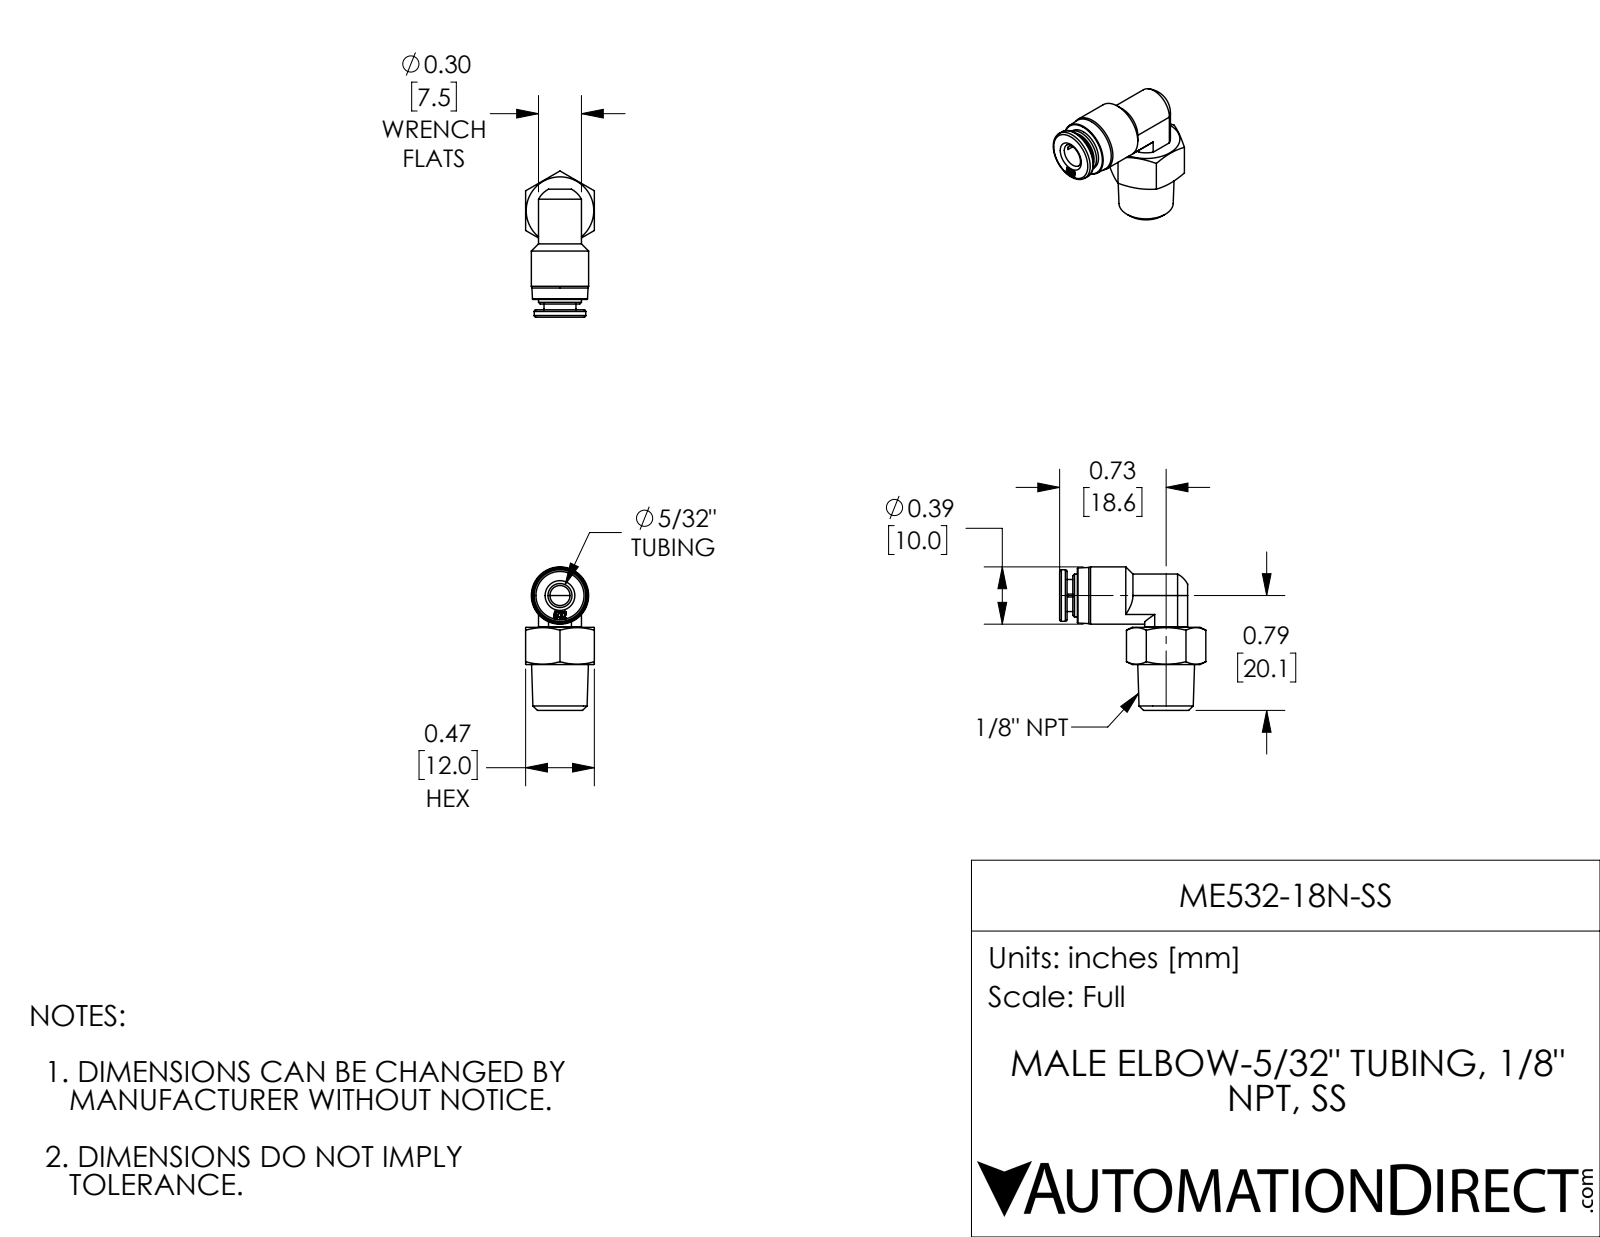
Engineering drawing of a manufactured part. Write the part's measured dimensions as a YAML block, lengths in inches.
part_name: "ME532-18N-SS"
step_written_by: "SolidWorks 2017 (AUTOMOTIVE_DESIGN)"
units: inches
bodies: {solids: 2, faces: 153, planar: 51, cylindrical: 27, other: 75}
overall_size: [1.005, 0.986, 0.472]
volume: 0.142
surface_area: 3.585
round_holes:
  - {diameter: 0.138, count: 2}
  - {diameter: 0.157, count: 1}
  - {diameter: 0.165, count: 1}
  - {diameter: 0.238, count: 1}
round_bosses_or_shafts:
  - {diameter: 0.394, count: 1}
  - {diameter: 0.354, count: 1}
  - {diameter: 0.295, count: 1}
  - {diameter: 0.236, count: 1}
  - {diameter: 0.22, count: 1}
partial_cylinders:
  - {radius: 0.167, count: 1}
face_to_face_distances: [0.472, 0.089, 0.384, 0.295, 0.256, 0.051, 0.315, 0.571, 0.88, 0.829]
